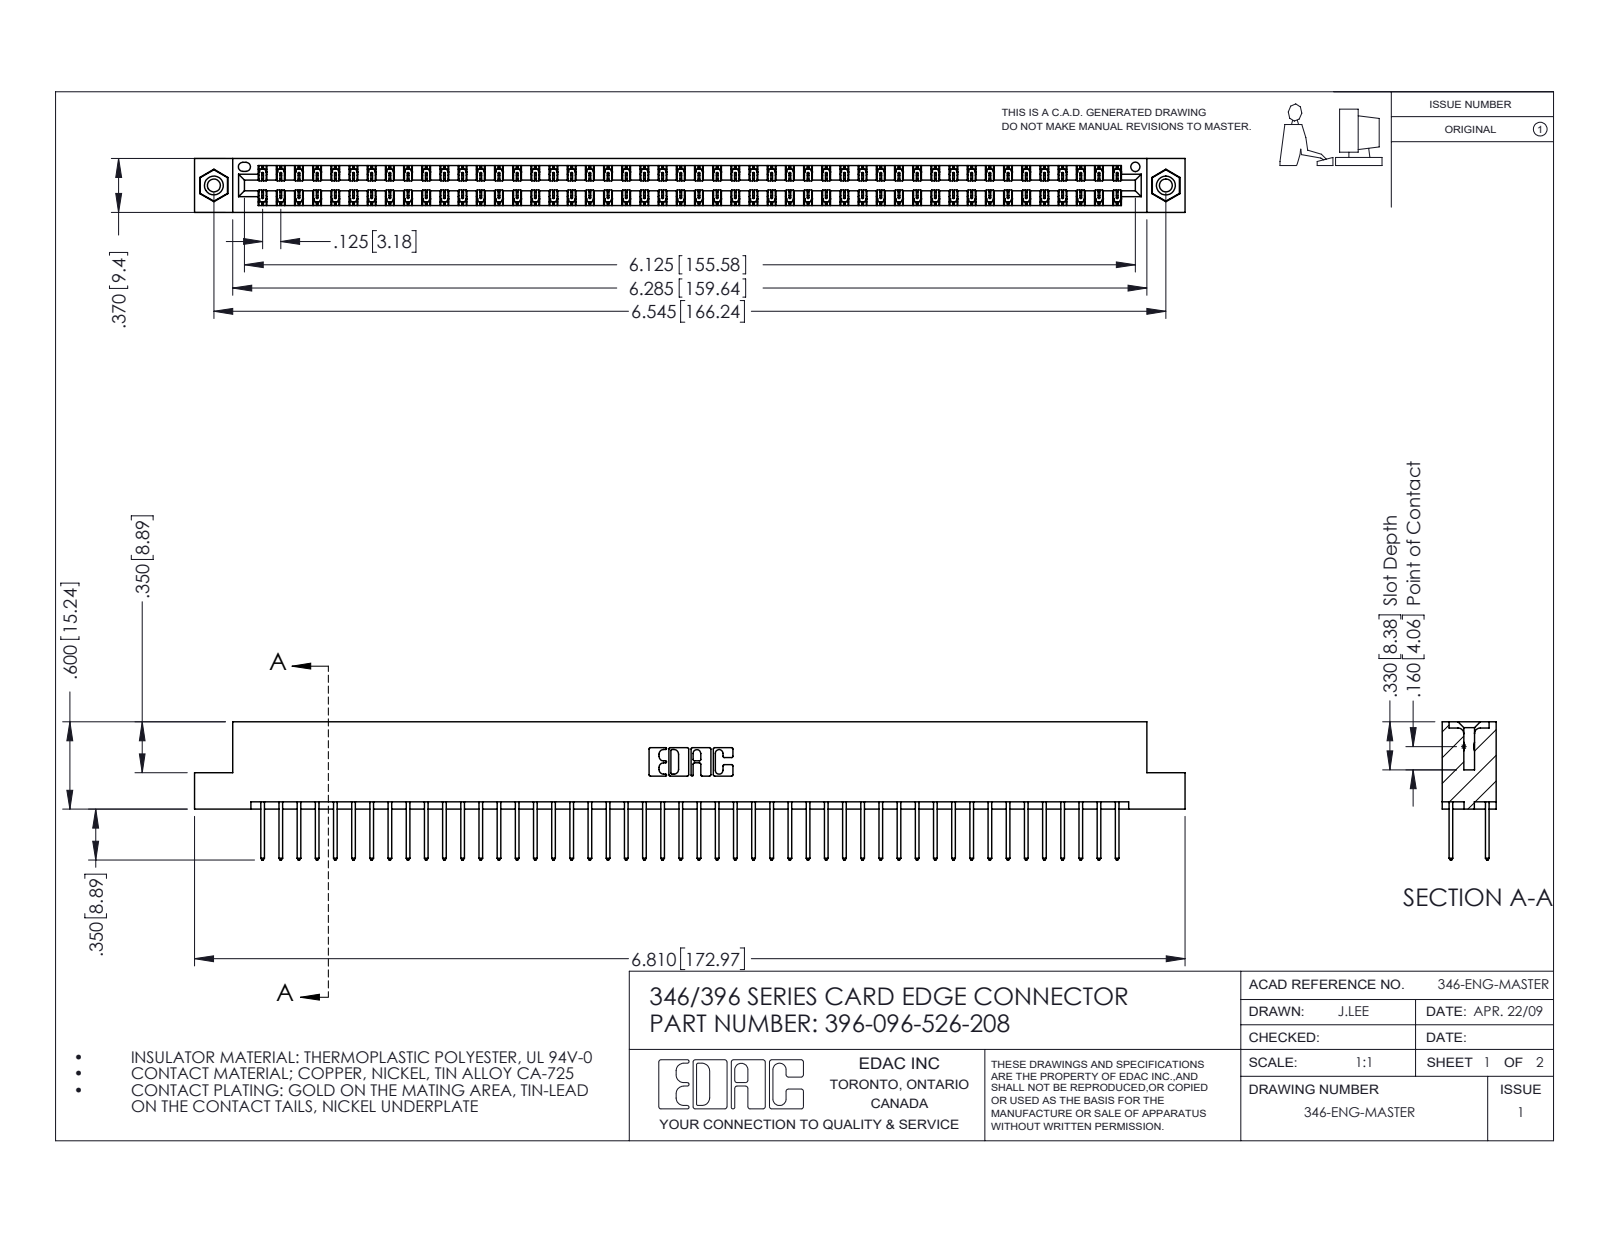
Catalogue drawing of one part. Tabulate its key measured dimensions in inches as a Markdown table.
| quantity | value |
| --- | --- |
| part name | 345-292-001_345-293-126; 396-096-526-208; 345-250-001_345-250-003-102; 346 Part_Flush Mounting Lugs - 0.156 Dia-TI |
| STEP written by | SolidWorks 2016 (CONFIG_CONTROL_DESIGN) |
| units | inches |
| bodies | 99 solids, 5174 faces (3468 planar, 1690 cylindrical, 16 other) |
| overall size | 6.81 × 0.95 × 0.37 |
| volume | 1.041 in³ |
| surface area | 37.63 in² |
| round holes (diameter × count) | 0.089 × 2, 0.125 × 2, 0.156 × 2, 0.064 × 1 |
| round bosses / shafts (diameter × count) | 0.155 × 2 |
| partial cylindrical surfaces (radius × count) | 0.006 × 144, 0.01 × 96, 0.01 × 22, 0.007 × 6, 0.031 × 6, 0.026 × 3, 0.014 × 2, 0.022 × 2 |
| main face-to-face distances | 0.048, 0.322, 0.25, 0.37, 0.072, 0.298, 0.025, 0.275, 0.148, 0.222 |
| hole center spacings | 0.246, 6.336, 6.545 |
